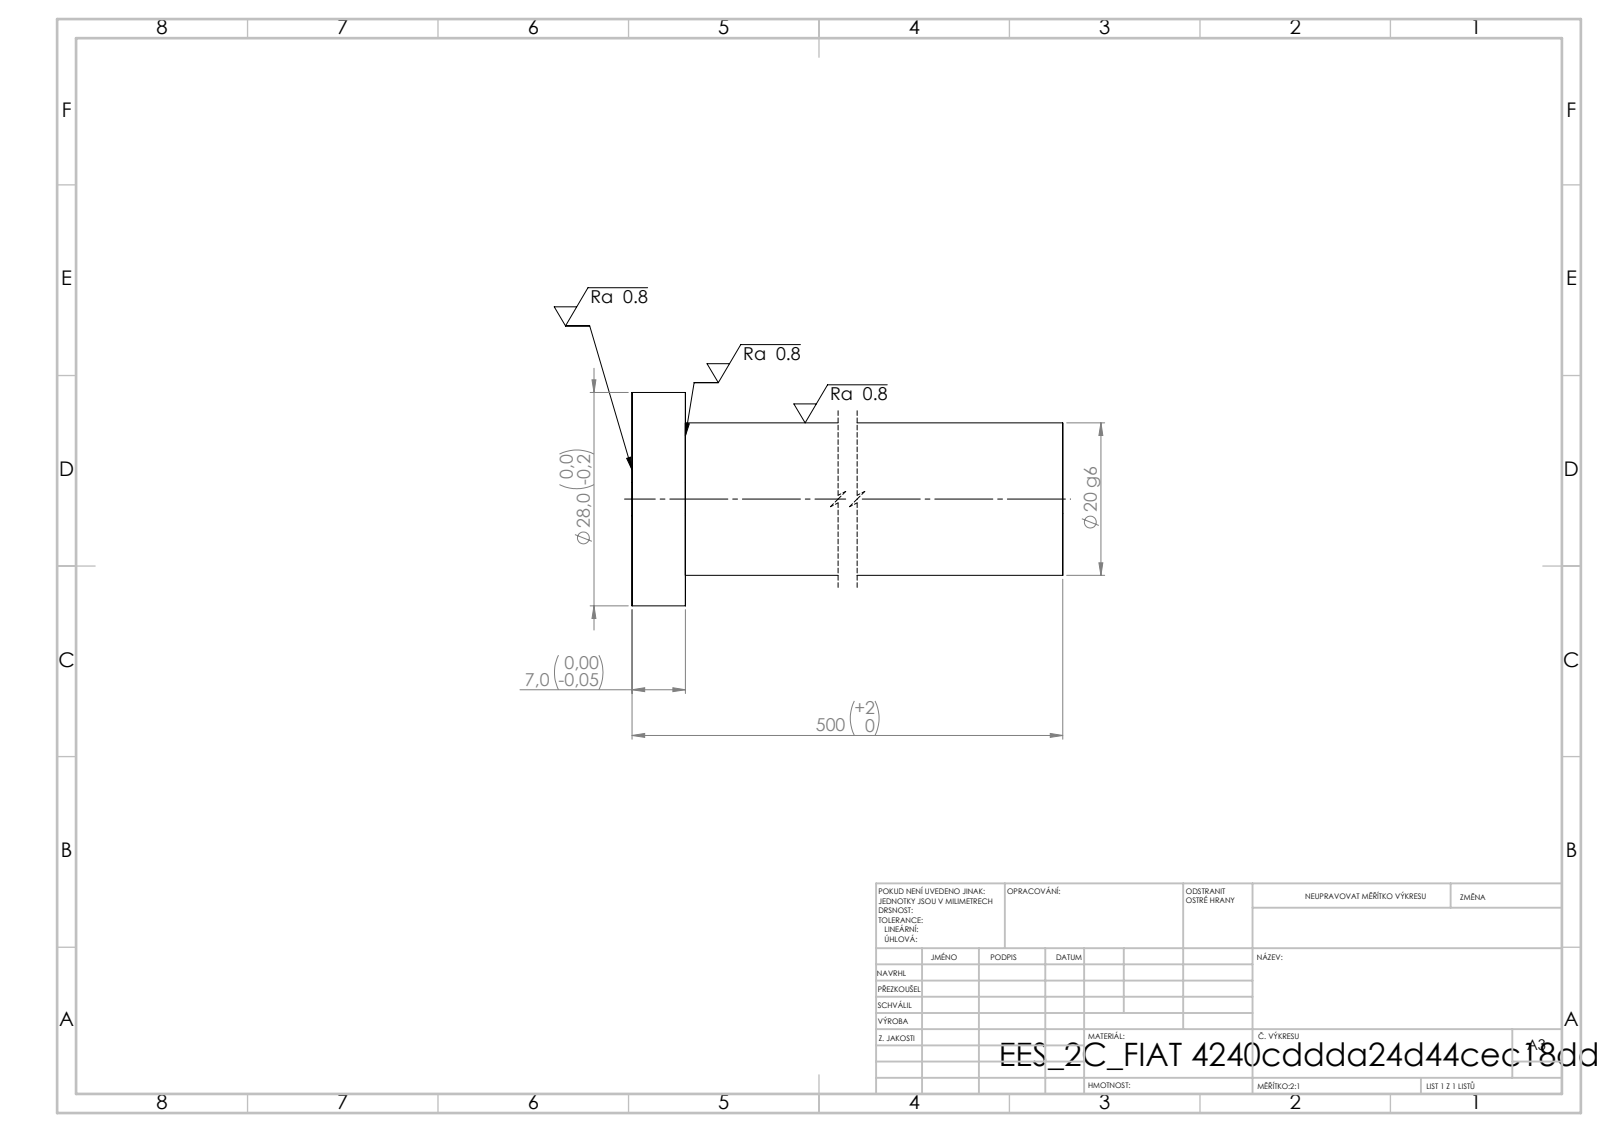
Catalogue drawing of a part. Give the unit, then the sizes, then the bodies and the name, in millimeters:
Units: millimetres
Overall size (bounding box): 500 × 28 × 28
Round bosses / shafts (diameter × count): ⌀28 ×1, ⌀20 ×1
Main face-to-face distances: 500, 7, 493
Volume: 159 191 mm³ · Surface area: 32 823 mm²
Bodies: 1 solid, 7 faces (3 planar, 4 cylindrical, 0 other)
STEP written by: SolidWorks 2019 (CONFIG_CONTROL_DESIGN)
